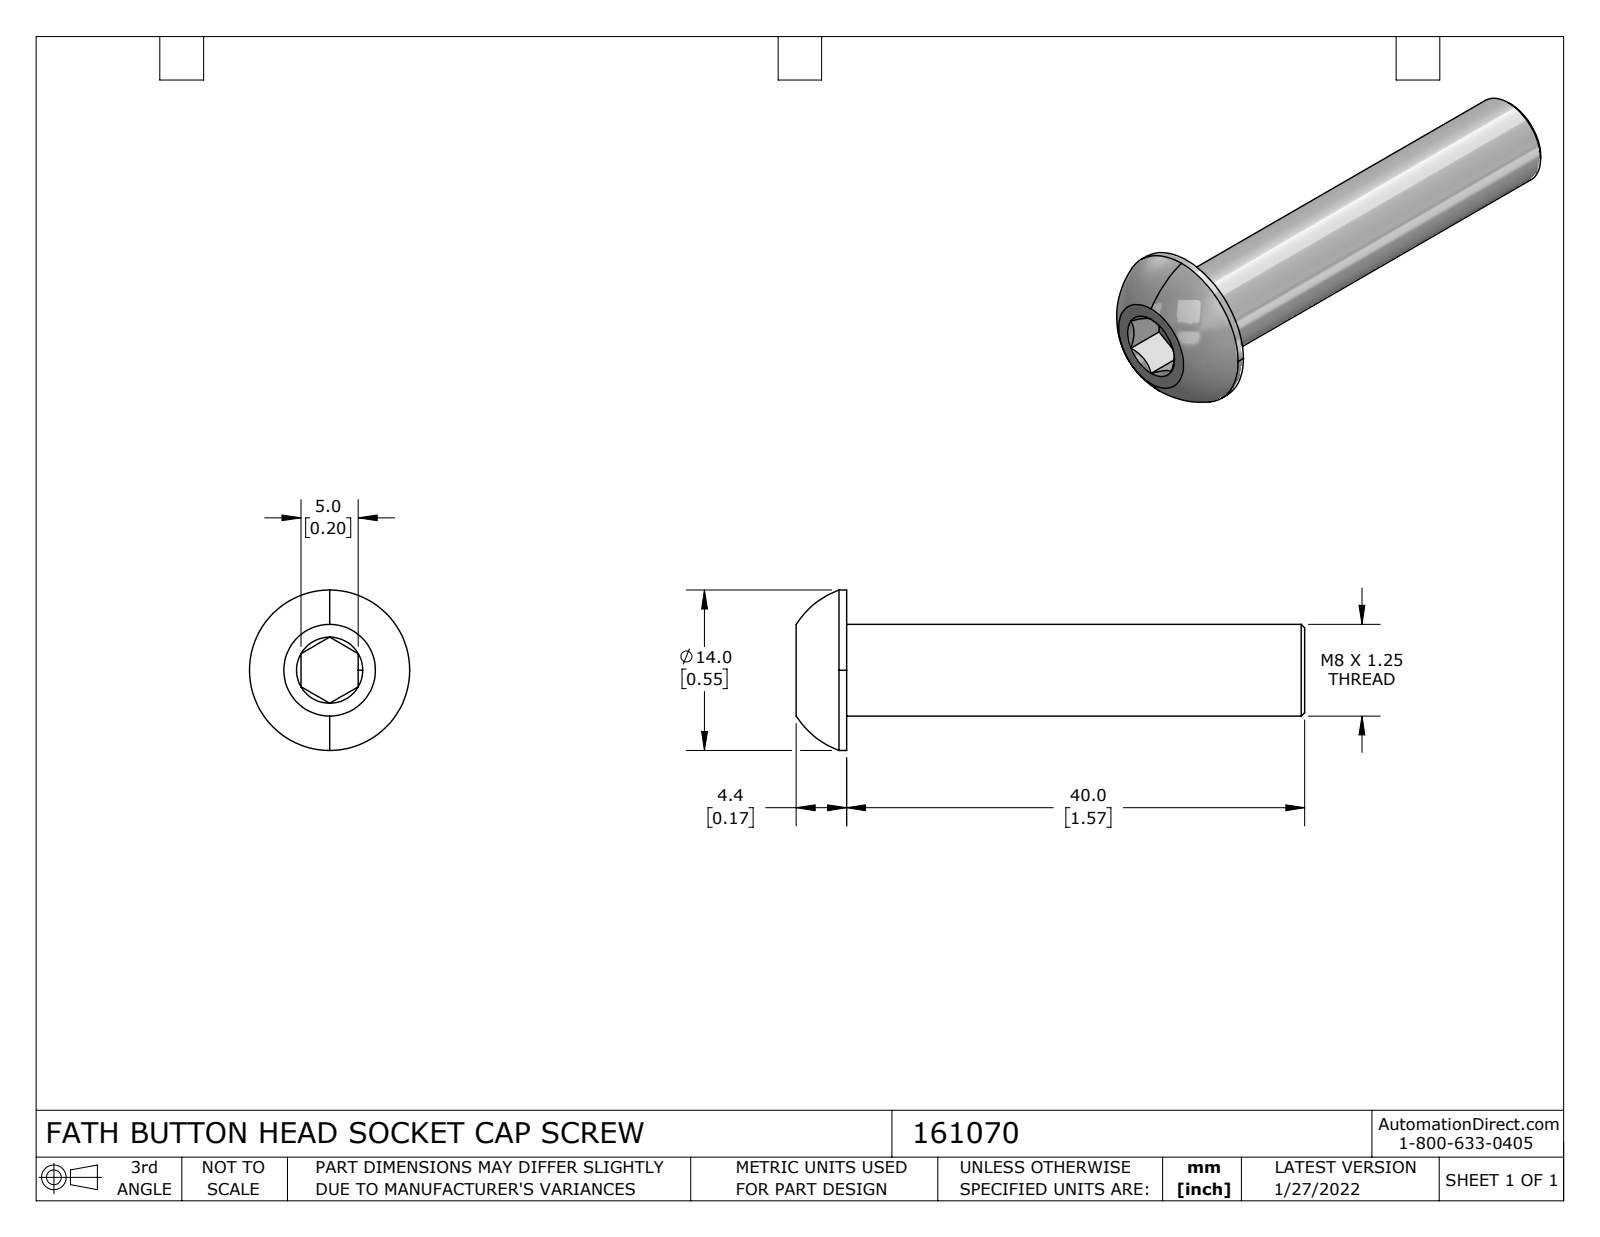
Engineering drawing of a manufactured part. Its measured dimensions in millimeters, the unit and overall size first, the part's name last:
Units: millimetres
Overall size (bounding box): 44.4 × 14 × 14
Round bosses / shafts (diameter × count): ⌀14 ×1, ⌀8 ×1
Main face-to-face distances: 40, 5, 44.4, 4.4, 40.9, 0.9, 3.5
Volume: 2 444 mm³ · Surface area: 1 467 mm²
Bodies: 1 solid, 25 faces (10 planar, 4 cylindrical, 11 other)
Part name (STEP PRODUCT): 161070
STEP written by: SolidWorks 2021 (CONFIG_CONTROL_DESIGN)
